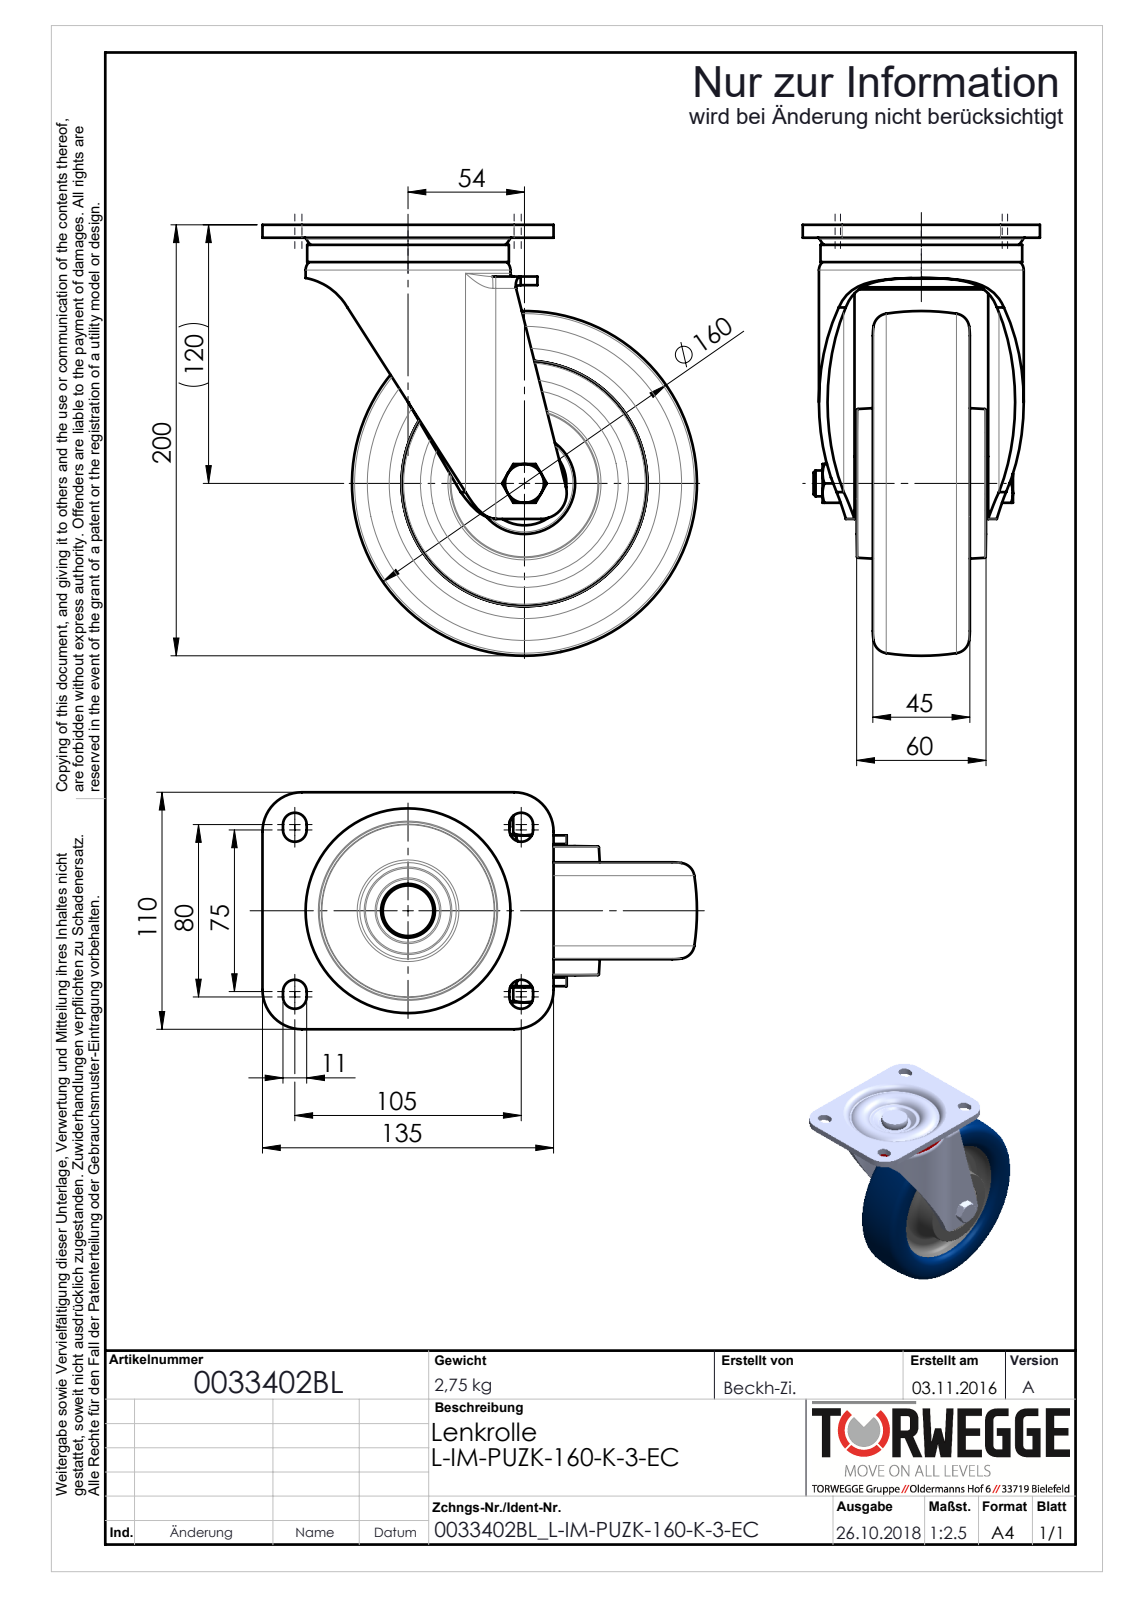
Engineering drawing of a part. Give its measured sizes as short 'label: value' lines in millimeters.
name: 0033402_L-IM-PUZK-160-K-3-EC
written by: SolidWorks 2016 (AUTOMOTIVE_DESIGN)
unit: mm
bodies: 0 solids, 674 faces (312 planar, 152 cylindrical, 210 other)
size: 201.5 × 200 × 110
holes: 1× ⌀10.2, 1× ⌀12, 1× ⌀12.2, 1× ⌀16.2, 1× ⌀20, 1× ⌀20.5, 1× ⌀38.9, 1× ⌀40, 1× ⌀40.2, 1× ⌀55.6, 1× ⌀80.46, 1× ⌀87
bosses: 2× ⌀18, 1× ⌀95, 1× ⌀93.54, 1× ⌀61.97, 1× ⌀28.1, 1× ⌀25, 1× ⌀19.9
rounds: 10× R5.5, 8× R0.31, 7× R0.17, 7× R0.51, 4× R0.1, 4× R0.72, 4× R0.78, 4× R18.29
face distances: 6, 4, 20, 10, 30, 2, 66, 26, 40, 70
